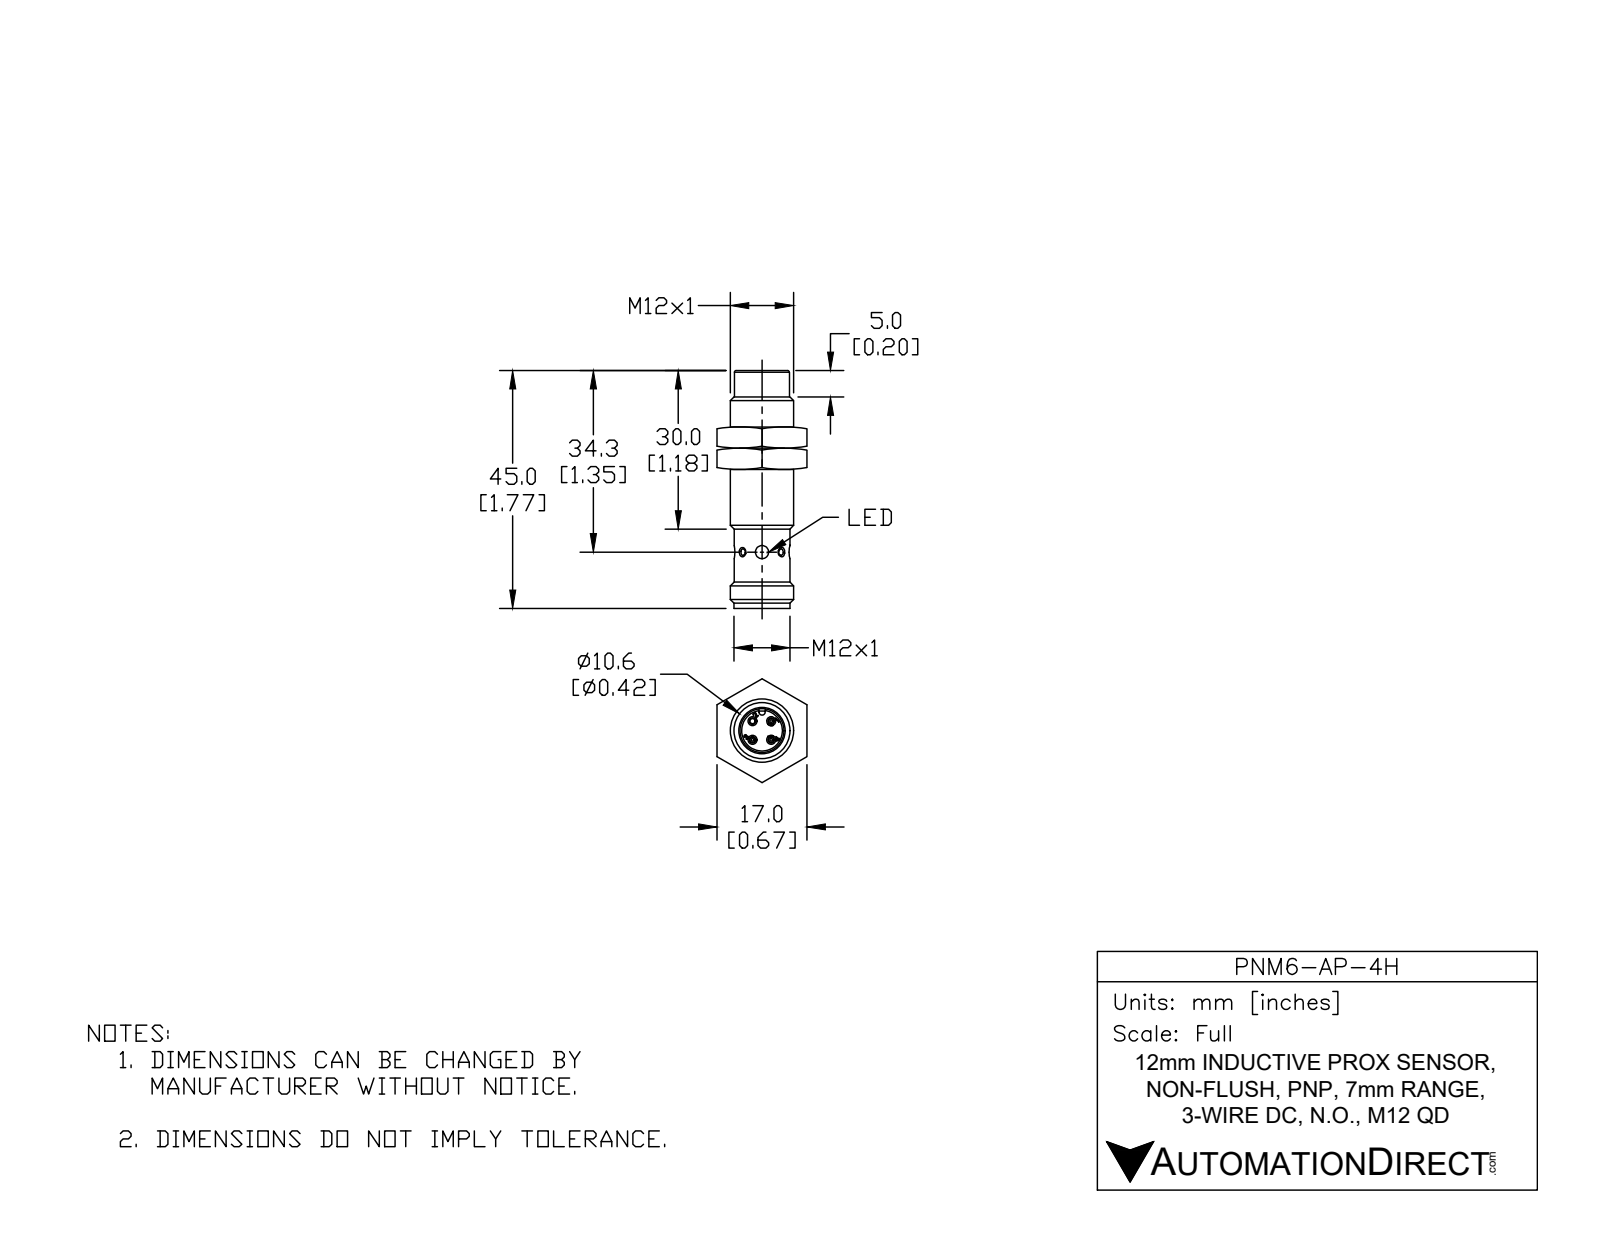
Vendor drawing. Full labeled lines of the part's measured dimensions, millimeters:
Part name (STEP PRODUCT): PNM6-AP-4H
STEP written by: SolidWorks 2017 (AUTOMOTIVE_DESIGN)
Units: millimetres
Bodies: 1 solid, 491 faces (117 planar, 138 cylindrical, 236 other)
Overall size (bounding box): 45 × 12 × 12
Volume: 4 050 mm³ · Surface area: 5 172 mm²
Round holes (diameter × count): ⌀1.1 ×3, ⌀1 ×2, ⌀2.5 ×2, ⌀1 ×1, ⌀1 ×1, ⌀8.3 ×1, ⌀10 ×1, ⌀10.2 ×1
Round bosses / shafts (diameter × count): ⌀1 ×6, ⌀12 ×1, ⌀10.6 ×1, ⌀10.5 ×1, ⌀10.2 ×1, ⌀10 ×1, ⌀9.9 ×1, ⌀9.7 ×1
Partial cylindrical surfaces — rounded edges, fillets, slot ends (radius × count): R0.1 ×36, R2 ×6, R0.6 ×1, R0.8 ×1, R4.1 ×1
Main face-to-face distances: 3, 33, 30, 0.5, 2.5, 32.5, 33.1, 36.1, 35.7, 3.1
Hole centre spacings: 2.5, 3.5, 5
